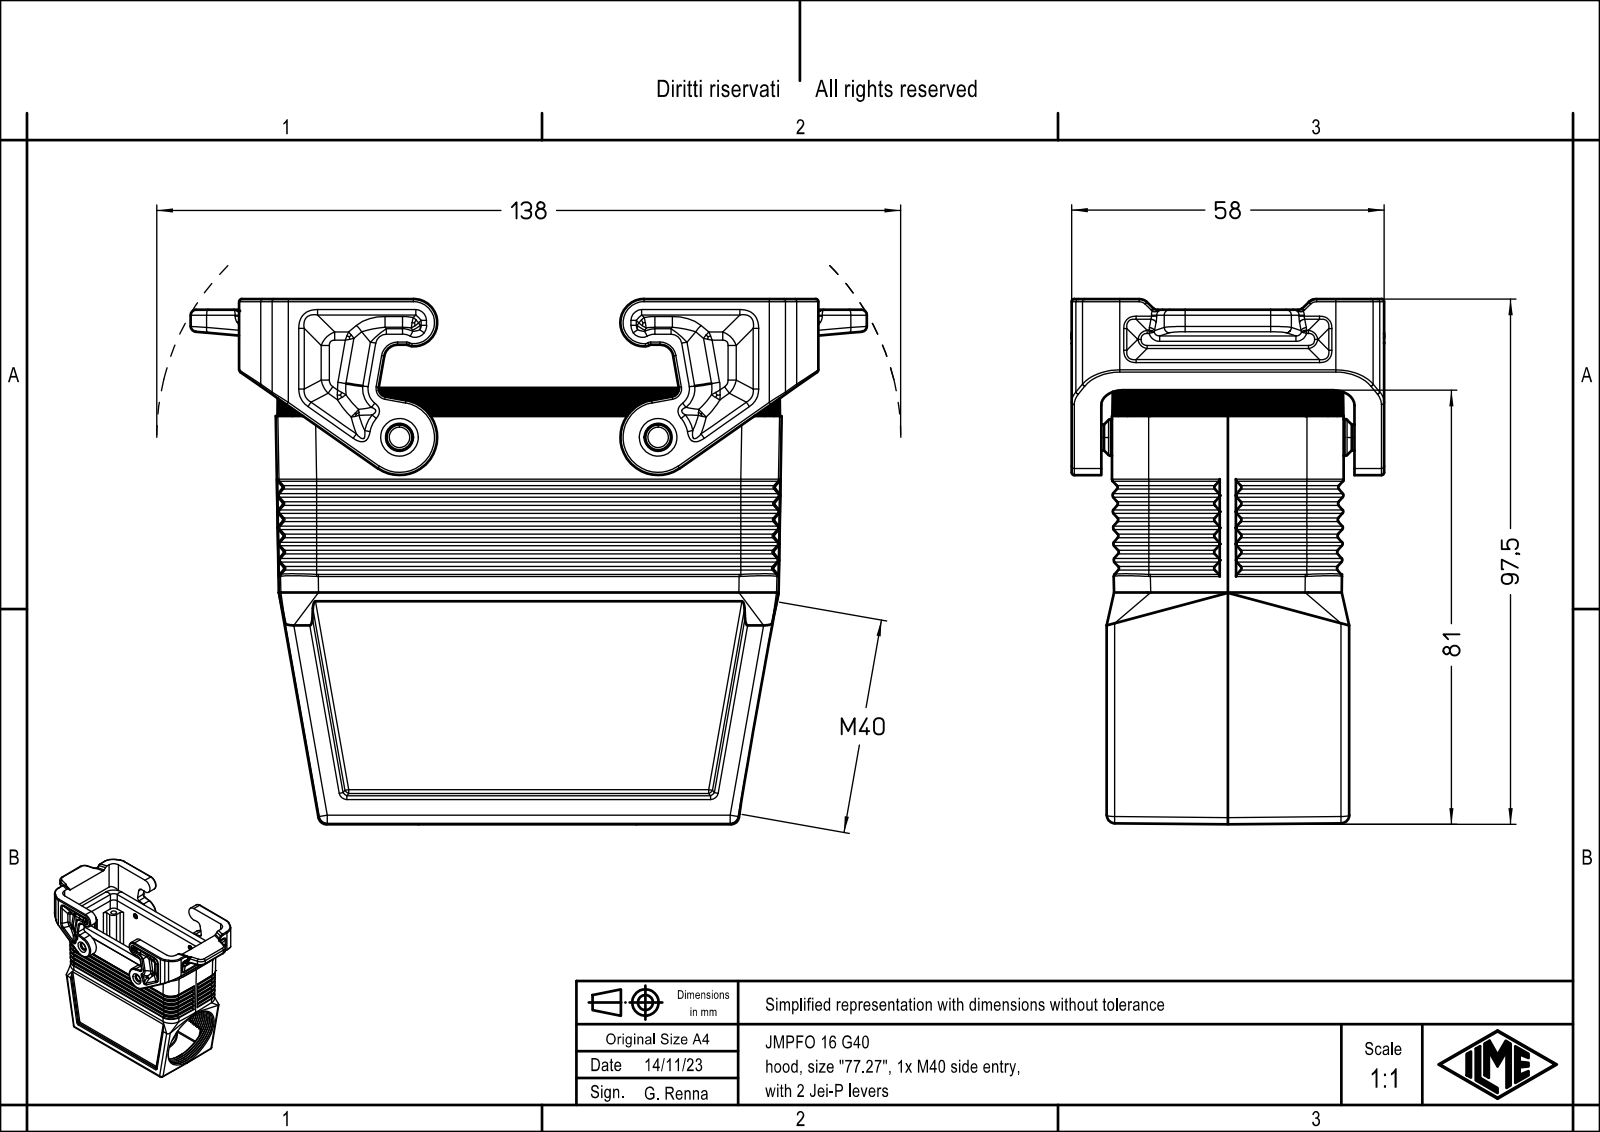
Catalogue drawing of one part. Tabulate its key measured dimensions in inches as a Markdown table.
| quantity | value |
| --- | --- |
| part name | JMPFO 16 G40 |
| STEP written by | Creo Elements/Direct Modeling 20.1B 02-Apr-2019 (C) Parametric Technology GmbH (AUTOMOTIVE_DESIGN) |
| units | inches |
| bodies | 1 solid, 1209 faces (334 planar, 395 cylindrical, 480 other) |
| overall size | 4.941 × 3.837 × 2.287 |
| volume | 6.879 in³ |
| surface area | 91.01 in² |
| round holes (diameter × count) | 0.118 × 4, 0.138 × 4, 0.189 × 2, 1.52 × 1 |
| round bosses / shafts (diameter × count) | 0.268 × 2 |
| partial cylindrical surfaces (radius × count) | 0.02 × 120, 0.039 × 48, 0.118 × 34, 0.059 × 26, 0.079 × 20, 0.013 × 15, 0.276 × 14, 0.157 × 12 |
| main face-to-face distances | 0.148, 1.545, 0.079, 1.398, 0.226, 1.693, 1.772, 1.624, 0.039, 0.157 |
| hole center spacings | 1.063, 3.051, 3.231, 1.89 |
